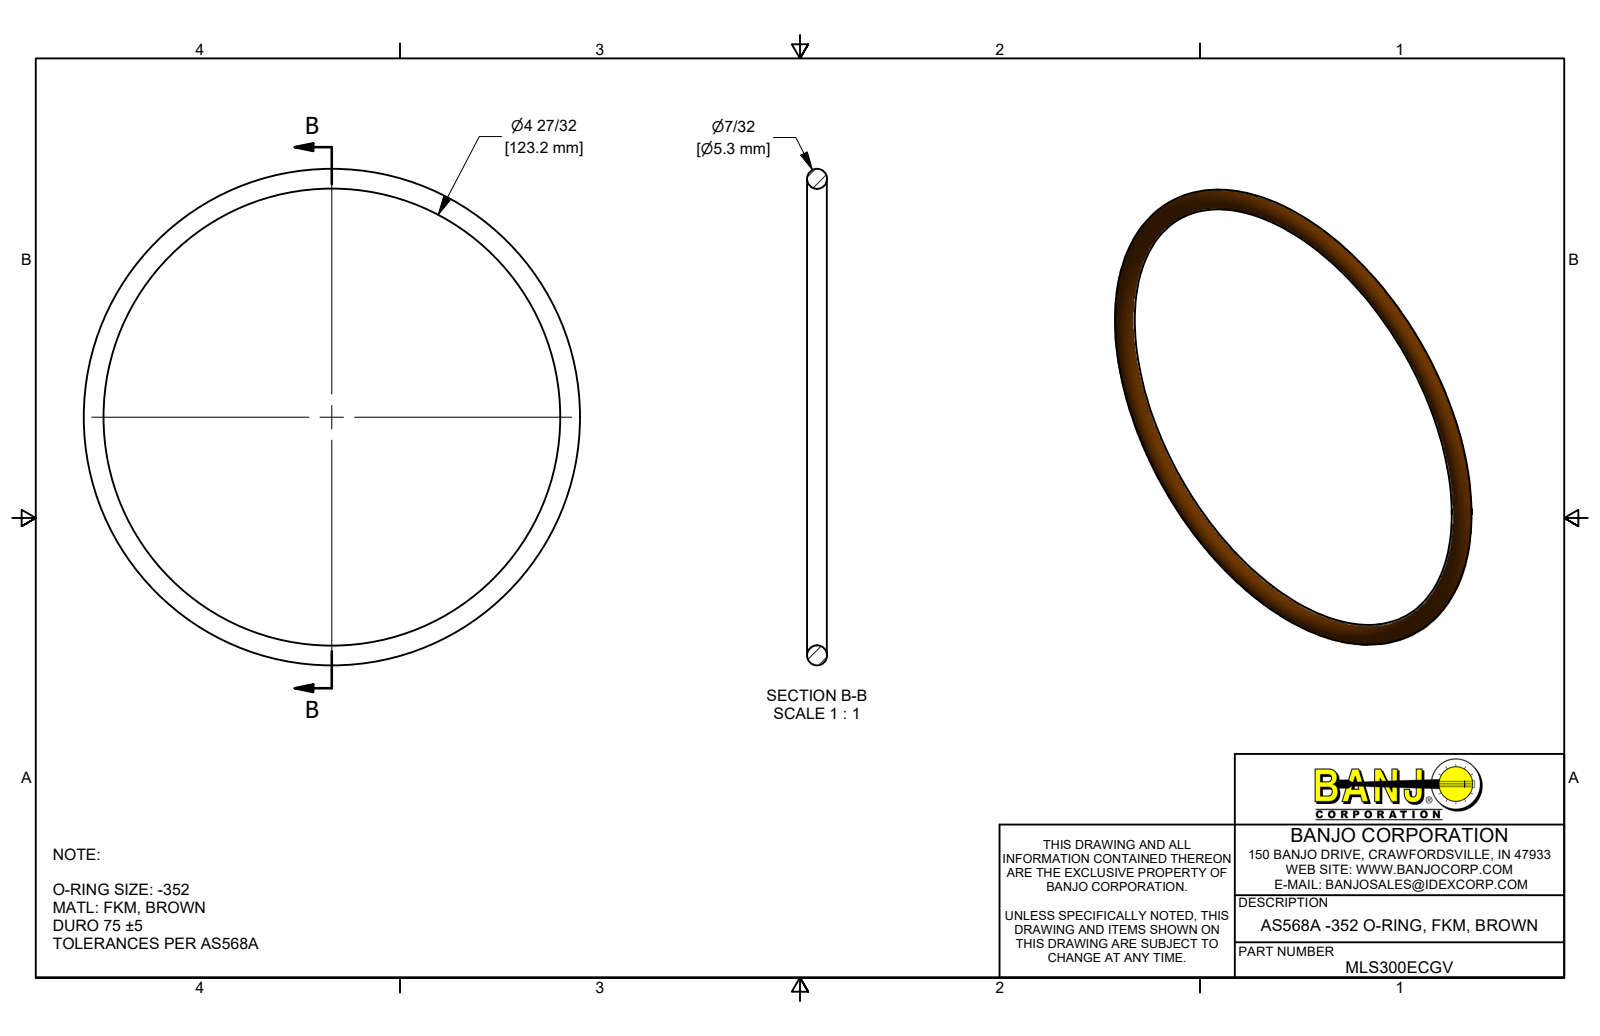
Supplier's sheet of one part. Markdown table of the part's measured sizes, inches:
| quantity | value |
| --- | --- |
| part name | MLS300ECGV |
| STEP written by | Autodesk Inventor 2019 (AUTOMOTIVE_DESIGN) |
| units | inches |
| bodies | 1 solid, 1 faces (0 planar, 0 cylindrical, 1 other) |
| overall size | 5.27 × 5.27 × 0.21 |
| volume | 0.551 in³ |
| surface area | 10.49 in² |
